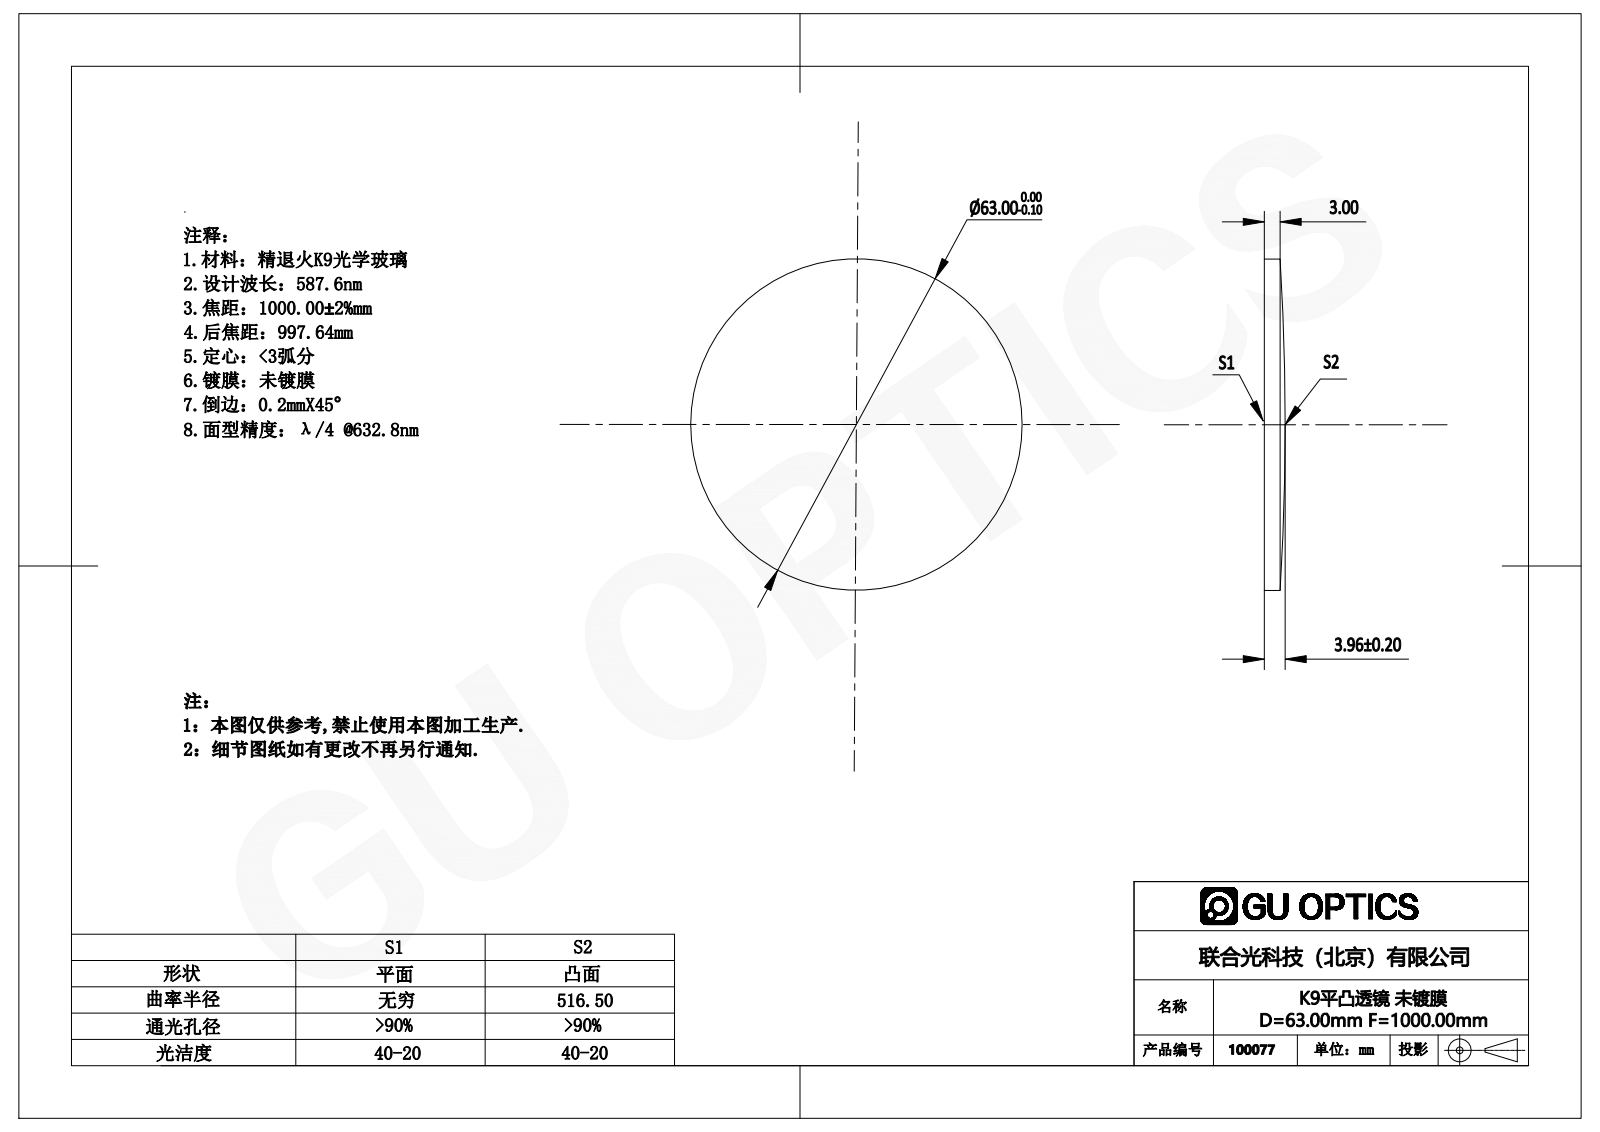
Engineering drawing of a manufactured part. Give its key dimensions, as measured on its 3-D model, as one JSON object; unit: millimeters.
{"part_name": "100077", "step_written_by": "SolidWorks 2016 (AUTOMOTIVE_DESIGN)", "units": "millimeters", "bodies": {"solids": 1, "faces": 5, "planar": 1, "cylindrical": 2, "other": 2}, "overall_size": [63, 63, 3.96], "volume_mm3": 10848, "surface_area_mm2": 6831, "round_bosses_or_shafts": [[63, 1]]}
